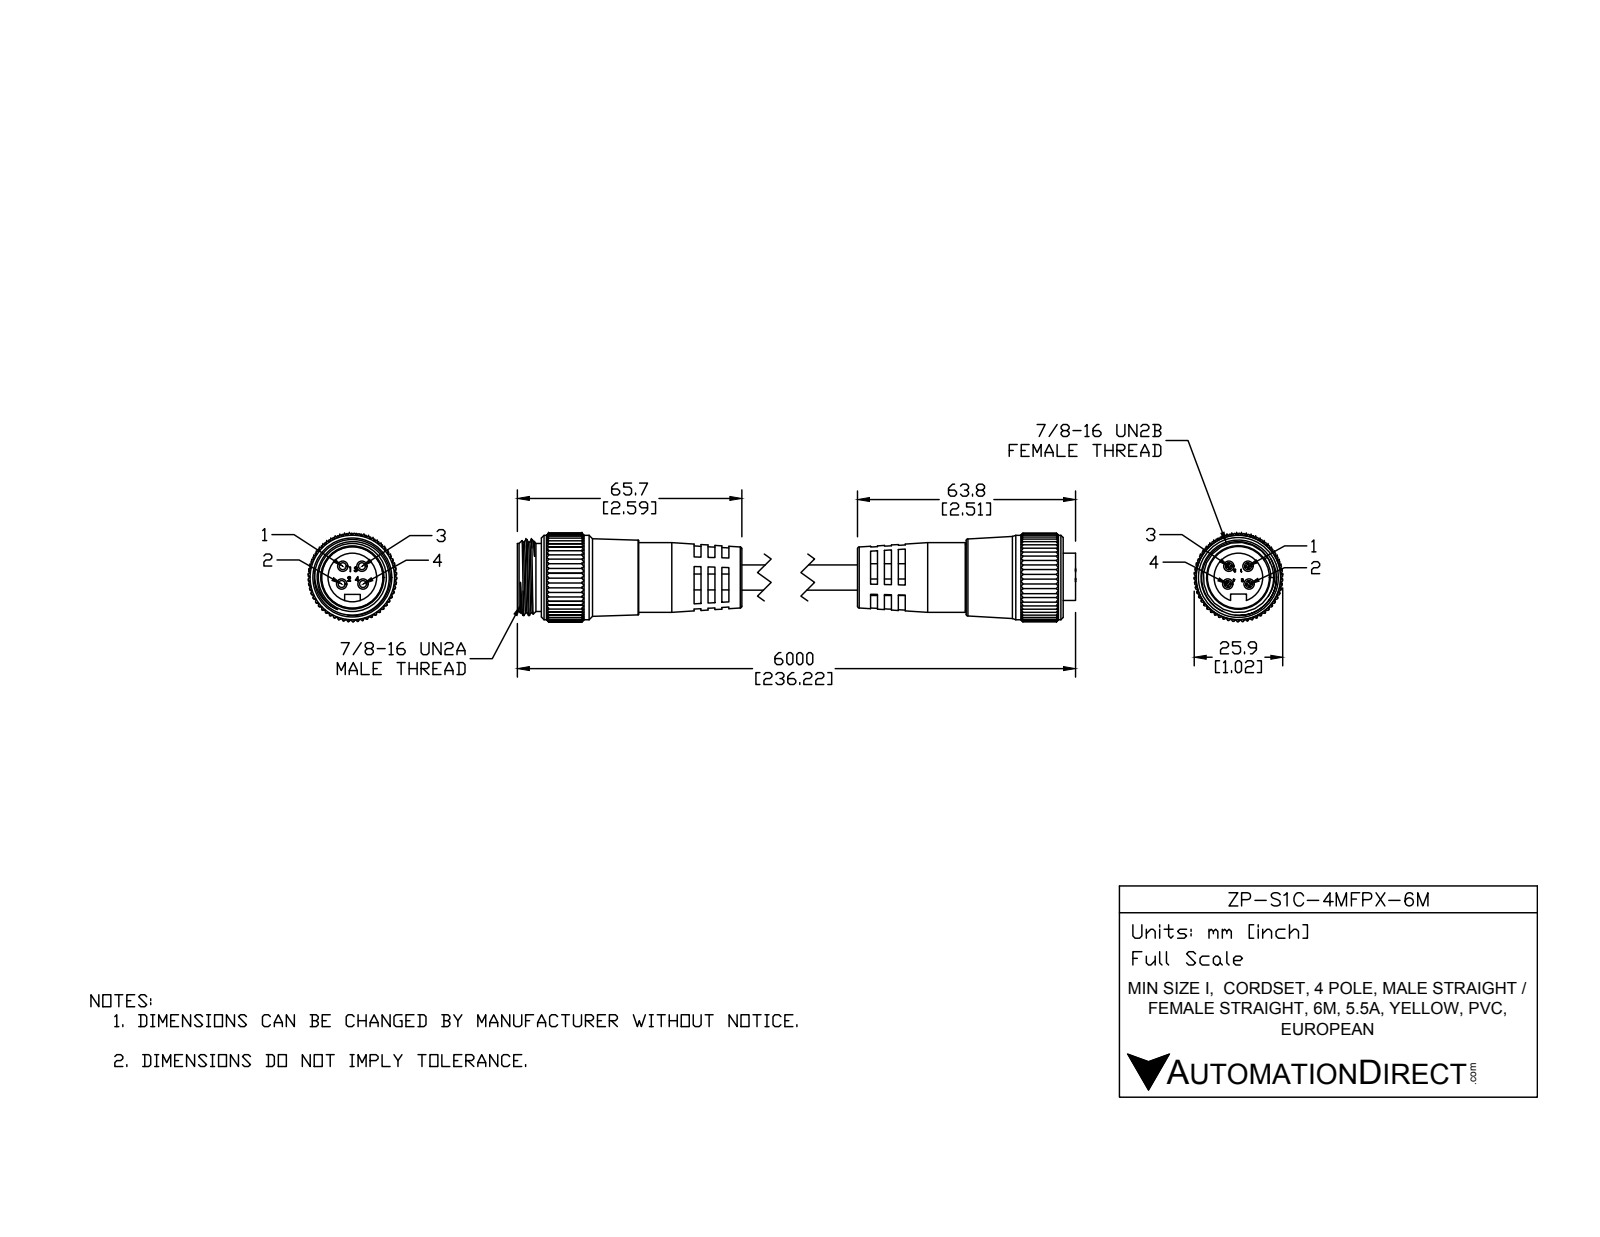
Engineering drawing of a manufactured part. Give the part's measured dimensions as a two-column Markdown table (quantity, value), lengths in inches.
| quantity | value |
| --- | --- |
| part name | ZP-S1C-4MFPX-6M |
| STEP written by | SolidWorks 2015 (AUTOMOTIVE_DESIGN) |
| units | inches |
| bodies | 8 solids, 1161 faces (427 planar, 634 cylindrical, 100 other) |
| overall size | 9.042 × 1.017 × 1.017 |
| volume | 3.141 in³ |
| surface area | 38.33 in² |
| round holes (diameter × count) | 0.12 × 4, 0.786 × 1, 0.805 × 1, 0.827 × 1 |
| round bosses / shafts (diameter × count) | 0.12 × 4, 0.079 × 4, 0.972 × 1, 0.875 × 1, 0.803 × 1, 0.768 × 1, 0.704 × 1, 0.56 × 1 |
| partial cylindrical surfaces (radius × count) | 0.01 × 165, 0.09 × 1, 0.207 × 1, 0.509 × 1 |
| main face-to-face distances | 0.079, 0.158, 4.633, 4.474, 0.159, 4.95, 2.356, 0.159, 4.791, 4.792 |
| hole center spacings | 0.144, 0.206, 0.17, 0.17, 0.22, 0.246, 0.311, 0.311 |
